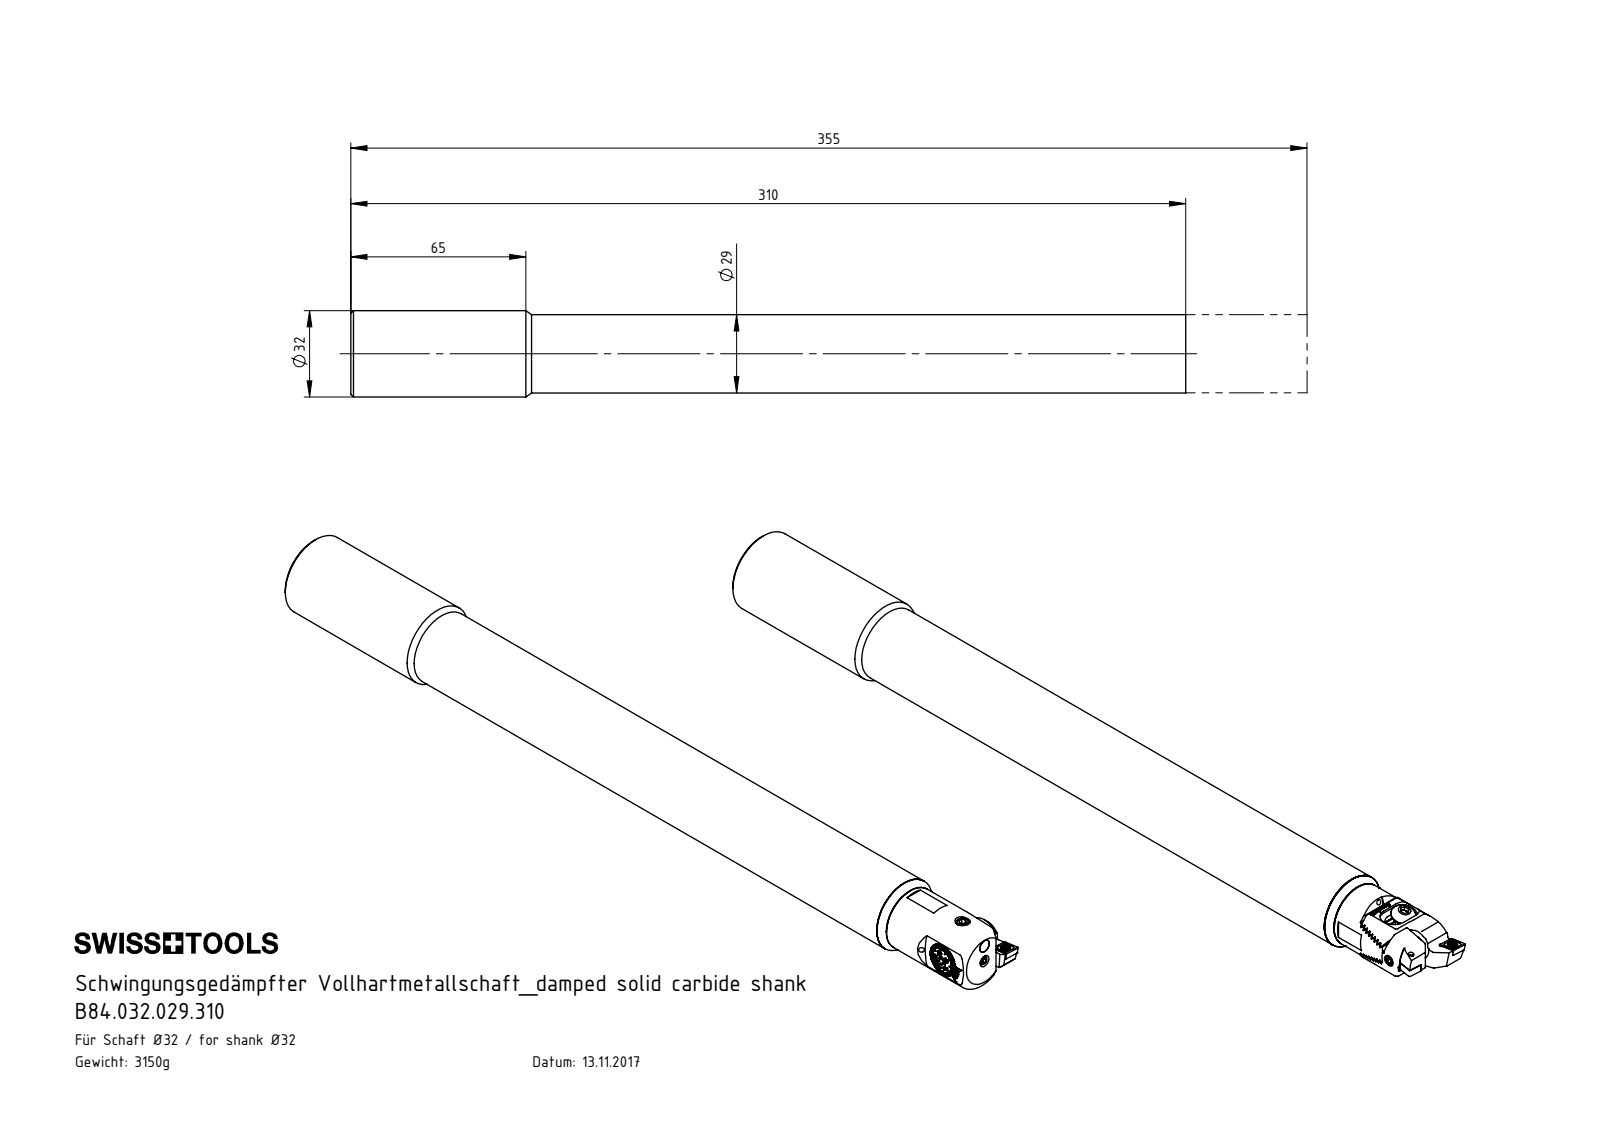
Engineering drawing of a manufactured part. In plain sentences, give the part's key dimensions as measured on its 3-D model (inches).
The part is named "HP5-F25.031.045_A; U32-HP5.029.310_A; DIN 3771 - 11x1; F25-BG1.012.013 (+8 more)". Its 3-D file was written by "SolidWorks 2017 (CONFIG_CONTROL_DESIGN)". It is 23 solids with 913 faces: 387 planar, 178 cylindrical and 348 other. Overall it measures 13.976 by 1.26 by 1.26 inches. Its volume is 14.14 cubic inches and its surface area 88.27 square inches. Round holes: 5 of diameter 0.079, 3 of diameter 0.165, 2 of diameter 0.081, 1 of diameter 0.083, 1 of diameter 0.094, 1 of diameter 0.106, 1 of diameter 0.11, 1 of diameter 0.118, 1 of diameter 0.13, 1 of diameter 0.152, 1 of diameter 0.197, 1 of diameter 0.217. Round bosses or shafts: 2 of diameter 0.197, 2 of diameter 0.195, 2 of diameter 0.098, 1 of diameter 1.26, 1 of diameter 1.142, 1 of diameter 0.984, 1 of diameter 0.63, 1 of diameter 0.511. Partial cylindrical surfaces (rounded edges, fillets, slot ends): 6 of radius 0.008, 5 of radius 0.014, 4 of radius 0.02, 2 of radius 0.052, 1 of radius 0.008, 1 of radius 0.014, 1 of radius 0.041, 1 of radius 0.049. The main face-to-face distances are 12.205, 0.118, 10.787, 1.417, 12.323, 1.535, 0.315, 0.591, 13.864, 3.077. The hole center spacings are 0.151, 0.157, 0.176, 0.268, 0.372, 0.656.
